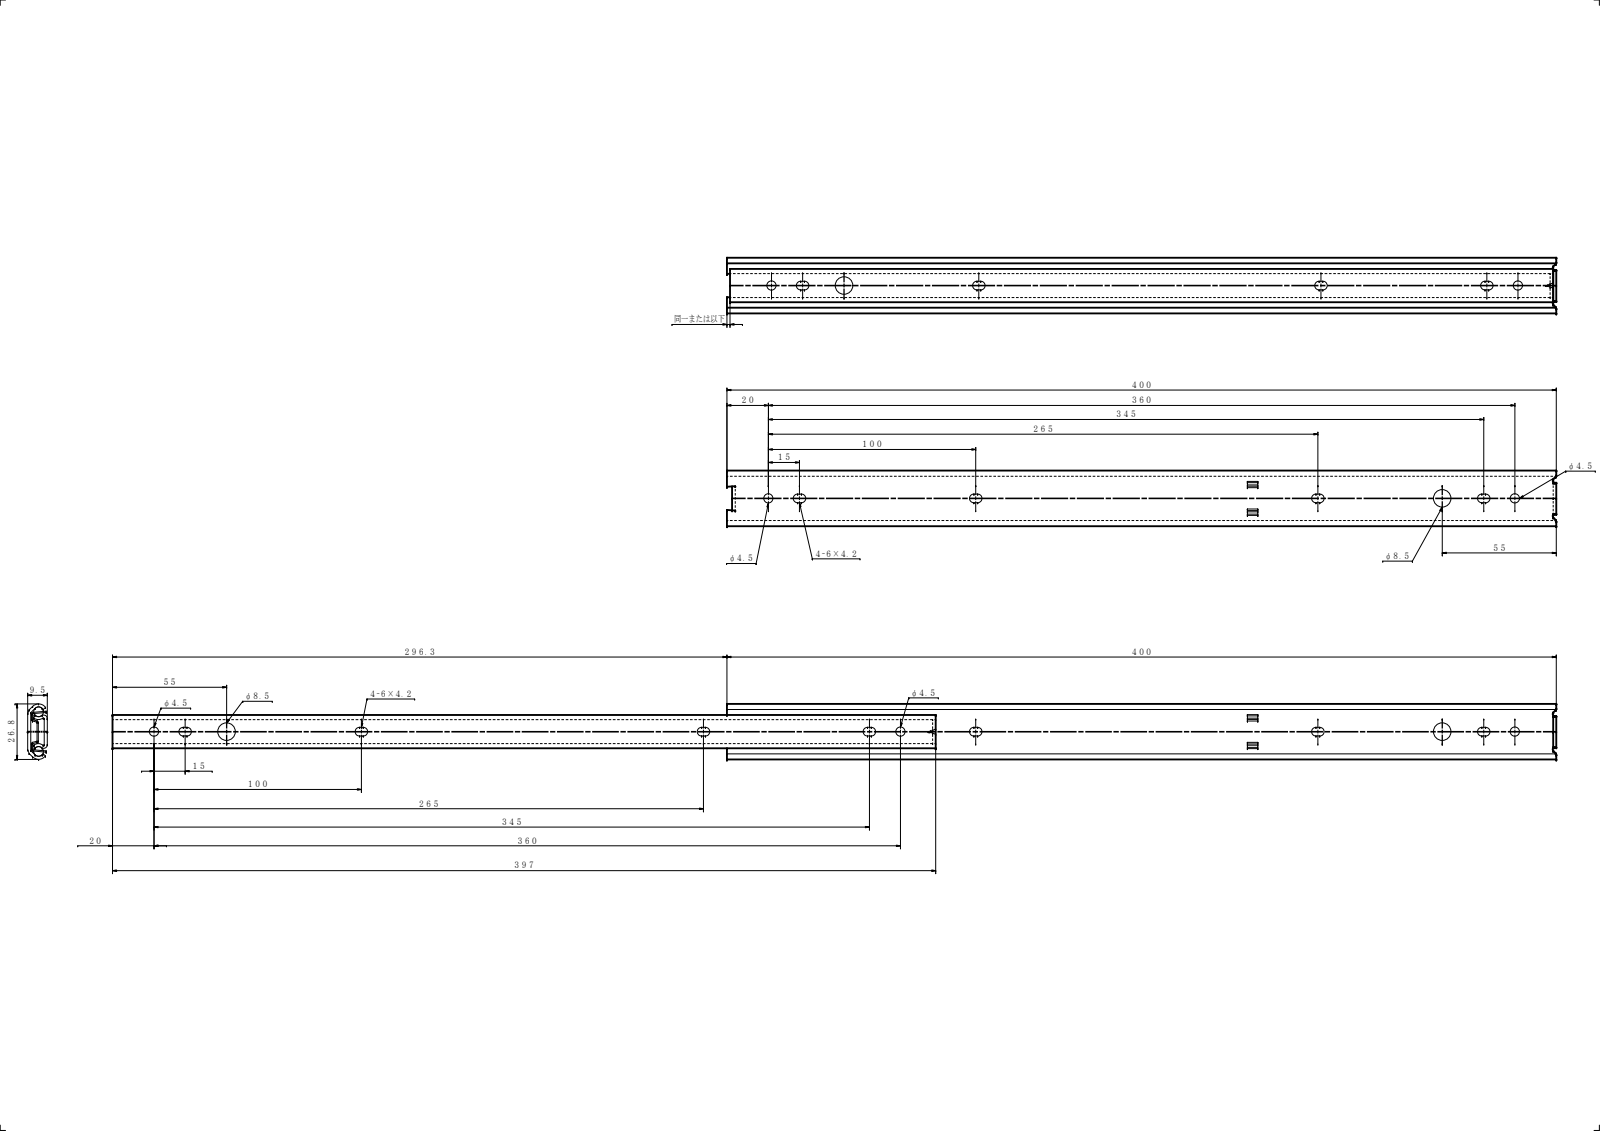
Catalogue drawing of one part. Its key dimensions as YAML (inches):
part_name: "U2721-400 OM; U2721_400; U2721-400 IM"
step_written_by: "SolidWorks 2019 (CONFIG_CONTROL_DESIGN)"
units: inches
bodies: {solids: 2, faces: 134, planar: 61, cylindrical: 73, other: 0}
overall_size: [27.413, 1.055, 0.374]
volume: 2.243
surface_area: 81.02
round_holes:
  - {diameter: 0.177, count: 4}
  - {diameter: 0.335, count: 2}
partial_cylinders:
  - {radius: 0.083, count: 16}
  - {radius: 0.079, count: 10}
  - {radius: 0.039, count: 5}
  - {radius: 0.02, count: 4}
  - {radius: 0.007, count: 2}
  - {radius: 0.051, count: 2}
  - {radius: 0.066, count: 2}
  - {radius: 0.094, count: 2}
face_to_face_distances: [0.059, 0.315, 0.374, 0.256, 11.783, 11.724, 15.591, 3.808, 11.843, 15.65]
hole_center_spacings: [1.378, 10.287, 11.665, 12.795, 14.173, 24.461, 2.508, 23.083]
